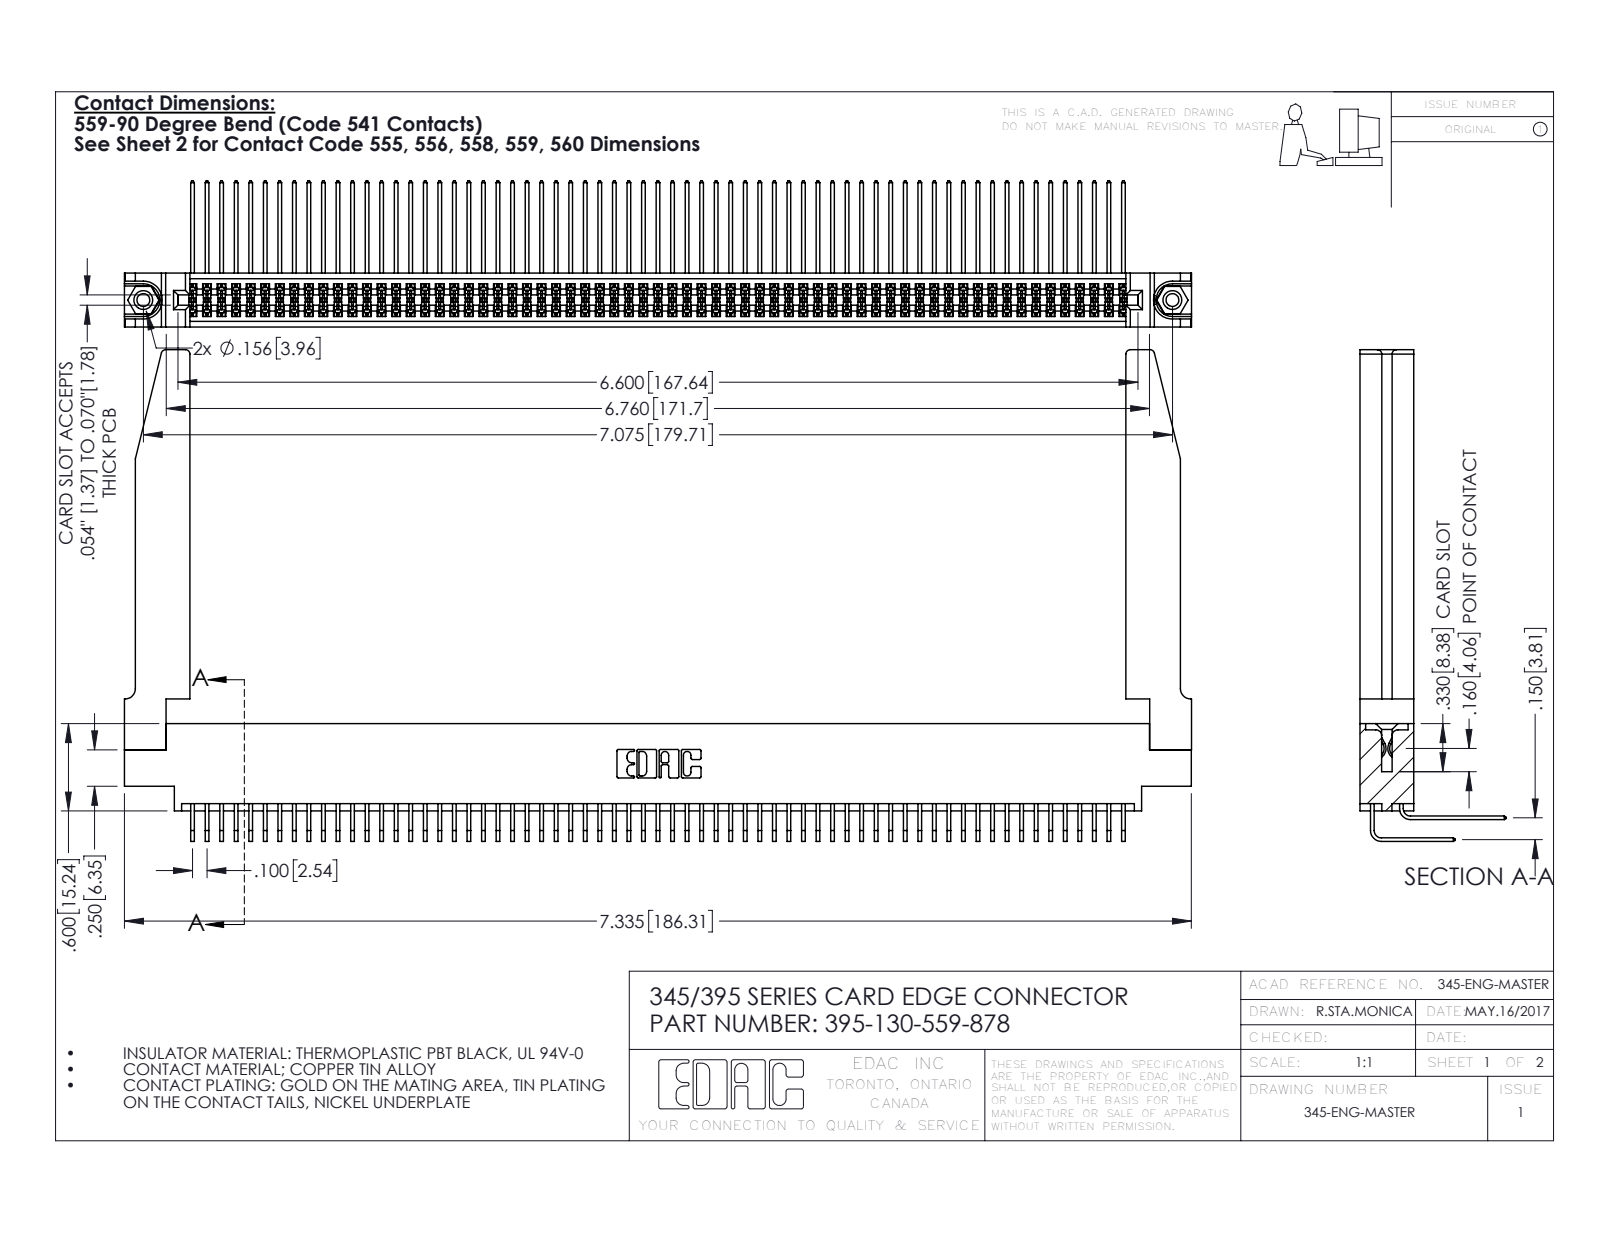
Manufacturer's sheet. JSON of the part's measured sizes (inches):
{"part_name": "345-250-001_345-250-001-102; 345-220-078_345-220-078; 345-292-001_559 Tail - 2; 345 Part_0.170 Offset - 0.156 Dia-TH (+2 more)", "step_written_by": "SolidWorks 2016 (CONFIG_CONTROL_DESIGN)", "units": "inches", "bodies": {"solids": 135, "faces": 7124, "planar": 4776, "cylindrical": 2296, "other": 52}, "overall_size": [7.336, 3.379, 1.005], "volume_in3": 1.631, "surface_area_in2": 60.4, "round_holes": [[0.089, 2], [0.125, 2], [0.156, 2], [0.064, 1]], "round_bosses_or_shafts": [[0.155, 2]], "partial_cylinders_radius": [[0.006, 196], [0.01, 22], [0.03, 8], [0.007, 6], [0.031, 6], [0.026, 3], [0.014, 2], [0.019, 2]], "face_to_face_distances": [0.072, 0.298, 0.37, 0.098, 0.272, 0.025, 0.2, 0.225, 0.15, 0.175], "hole_center_spacings": [0.27, 6.839, 7.075]}
